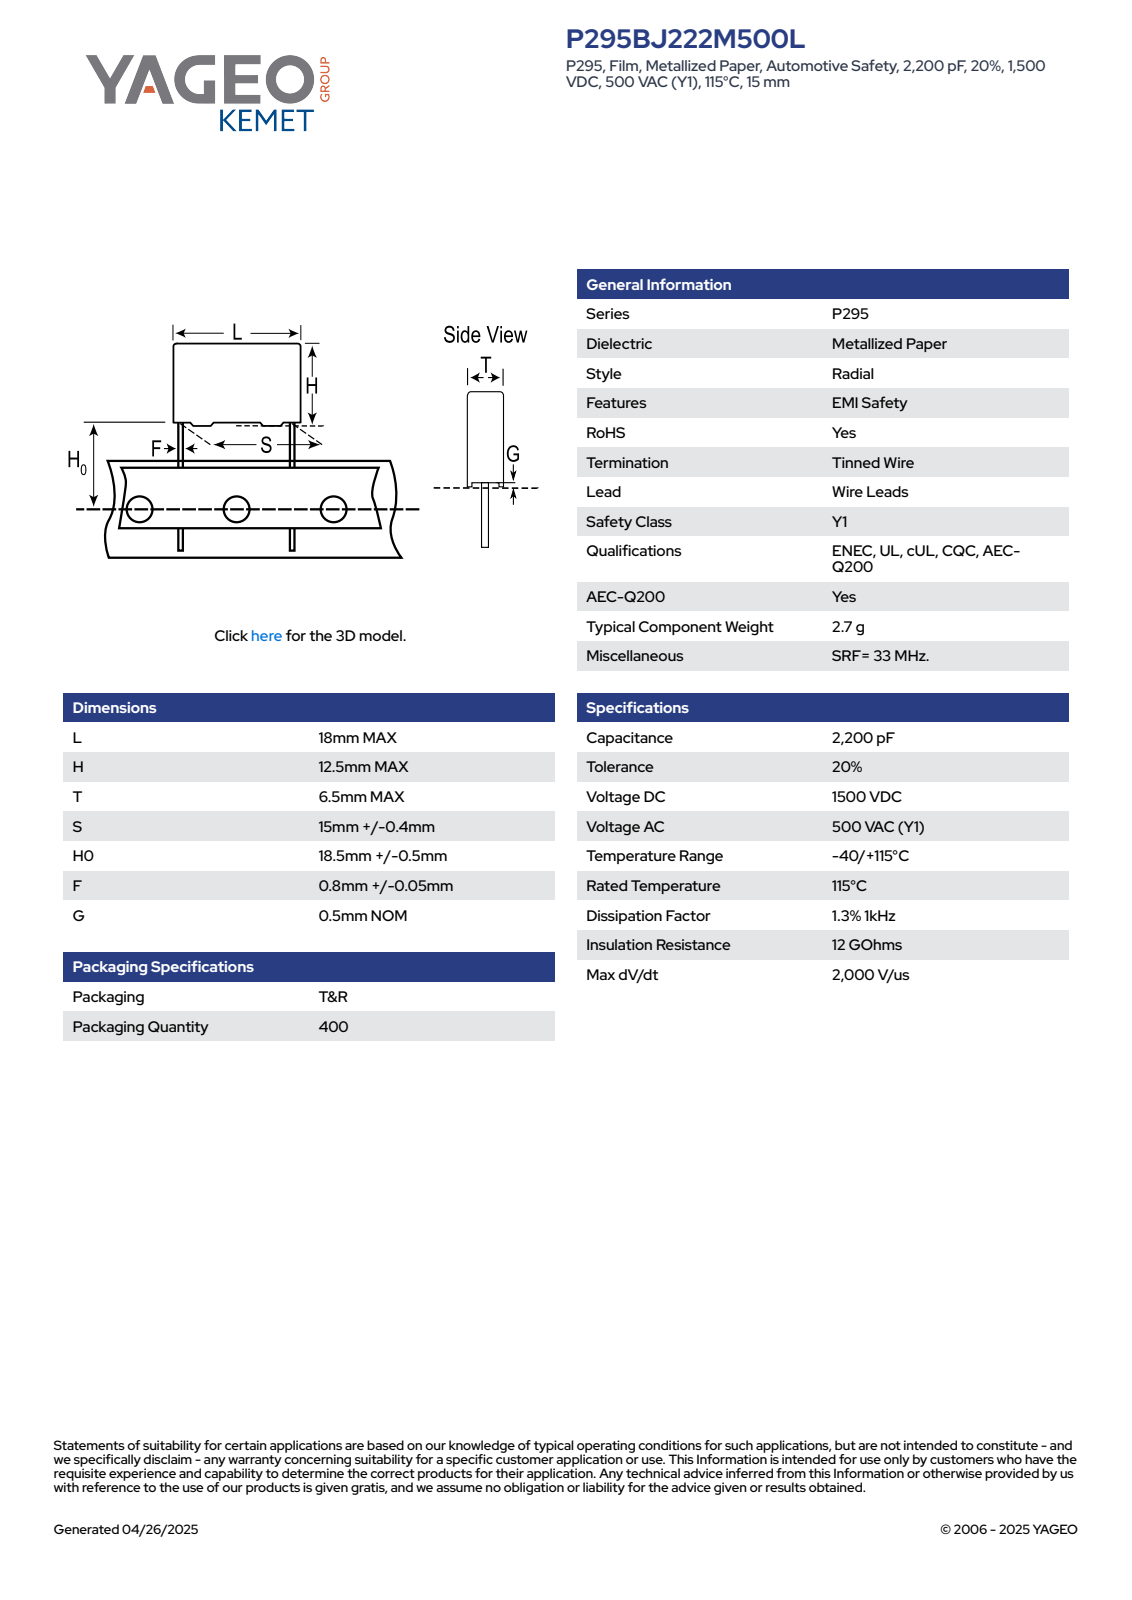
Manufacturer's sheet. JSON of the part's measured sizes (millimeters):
{"part_name": "CFR_RBG_18X12.5X6.5_L18H12.5T6.5S15H019F0.85G0.5", "step_written_by": "SolidWorks 2014 (AUTOMOTIVE_DESIGN)", "units": "millimeters", "bodies": {"solids": 4, "faces": 89, "planar": 81, "cylindrical": 8, "other": 0}, "overall_size": [31.5, 18, 6.5], "volume_mm3": 1426, "surface_area_mm2": 963, "round_bosses_or_shafts": [[0.85, 2]], "partial_cylinders_radius": [[0.5, 4]], "face_to_face_distances": [6.5, 12, 18, 0.37, 6.13, 0.5, 12.5, 5.76, 19, 19.5]}
